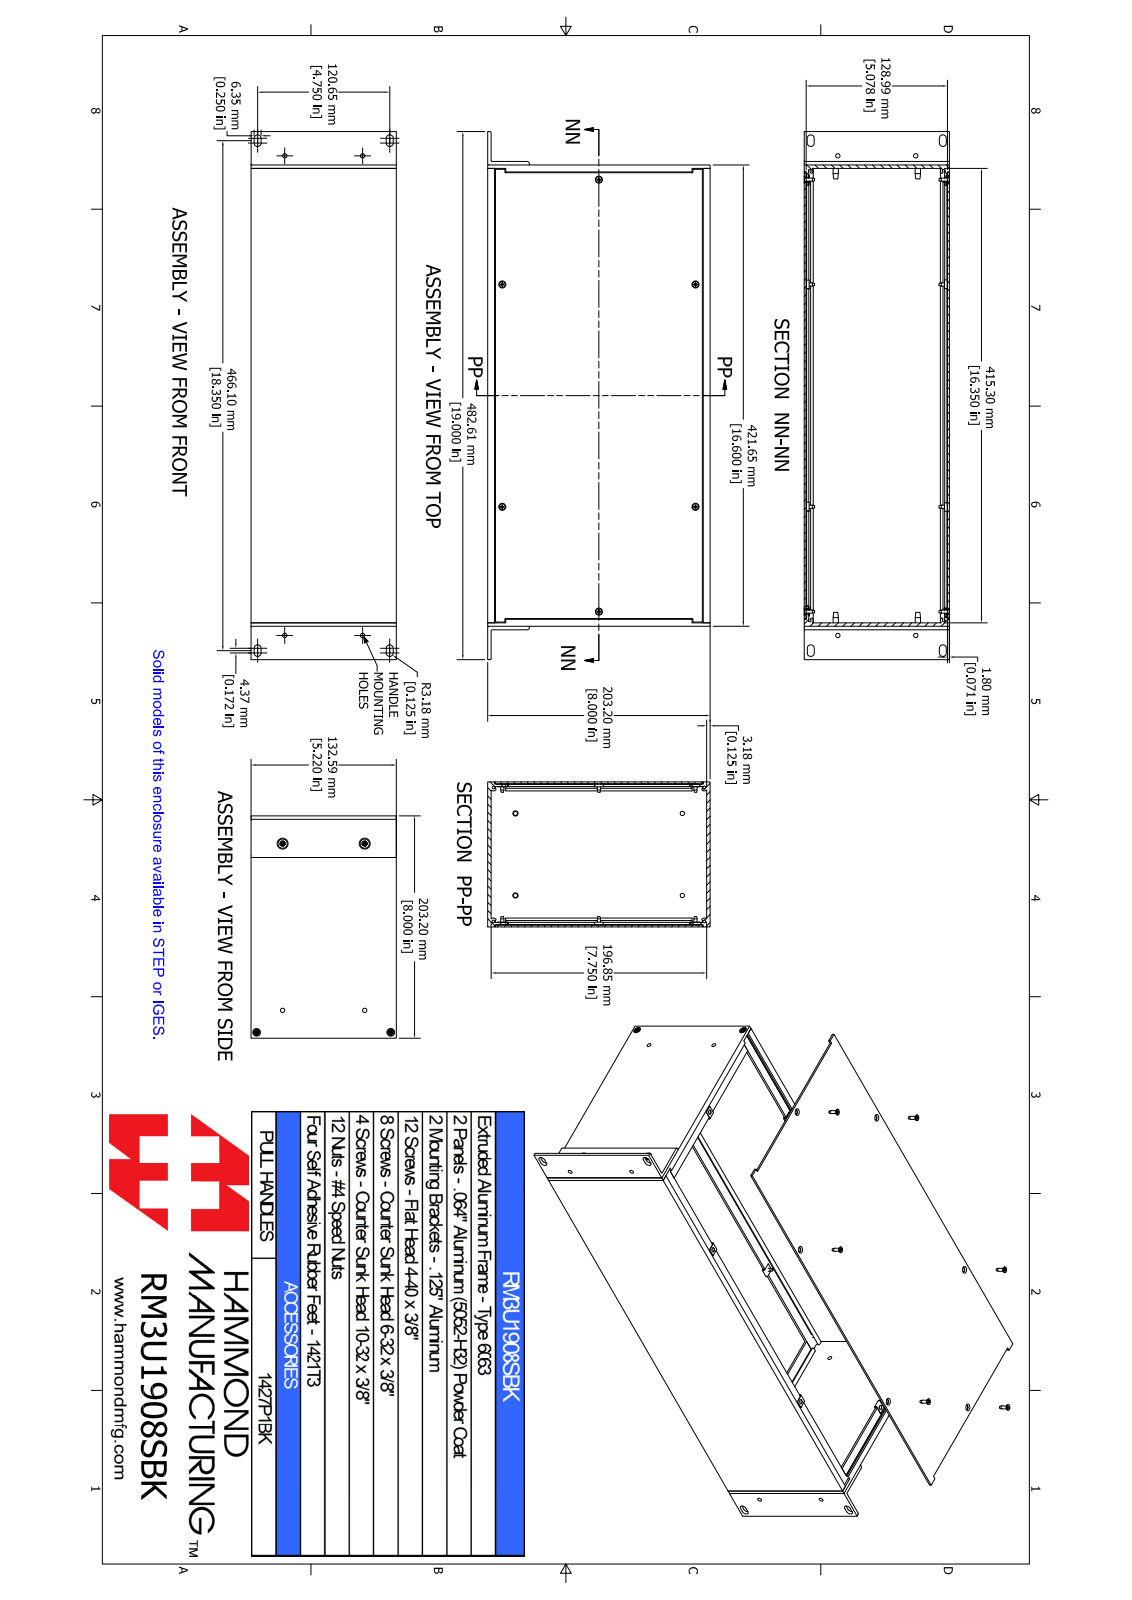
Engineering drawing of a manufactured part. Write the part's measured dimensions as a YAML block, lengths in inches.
part_name: "RM3U1908SBK"
step_written_by: "SolidWorks 2021 (AUTOMOTIVE_DESIGN)"
units: inches
bodies: {solids: 44, faces: 1184, planar: 564, cylindrical: 188, other: 432}
overall_size: [19, 8, 5.221]
volume: 58.39
surface_area: 1205
round_holes:
  - {diameter: 0.098, count: 6}
  - {diameter: 0.157, count: 6}
  - {diameter: 0.169, count: 6}
  - {diameter: 0.138, count: 4}
  - {diameter: 0.156, count: 4}
  - {diameter: 0.157, count: 4}
  - {diameter: 0.197, count: 4}
round_bosses_or_shafts:
  - {diameter: 0.214, count: 6}
  - {diameter: 0.112, count: 6}
  - {diameter: 0.333, count: 4}
  - {diameter: 0.238, count: 4}
  - {diameter: 0.19, count: 4}
  - {diameter: 0.138, count: 4}
partial_cylinders:
  - {radius: 0.039, count: 18}
  - {radius: 0.125, count: 16}
  - {radius: 0.049, count: 12}
  - {radius: 0.037, count: 8}
  - {radius: 0.05, count: 8}
  - {radius: 0.038, count: 4}
  - {radius: 0.079, count: 2}
face_to_face_distances: [0.071, 5.149, 0.125, 5.22, 0.125, 5.078, 8, 7.875, 7.75, 7.875]
hole_center_spacings: [6.854, 6, 7.824, 1.224, 1.224, 2.8, 2.952, 2.953]
